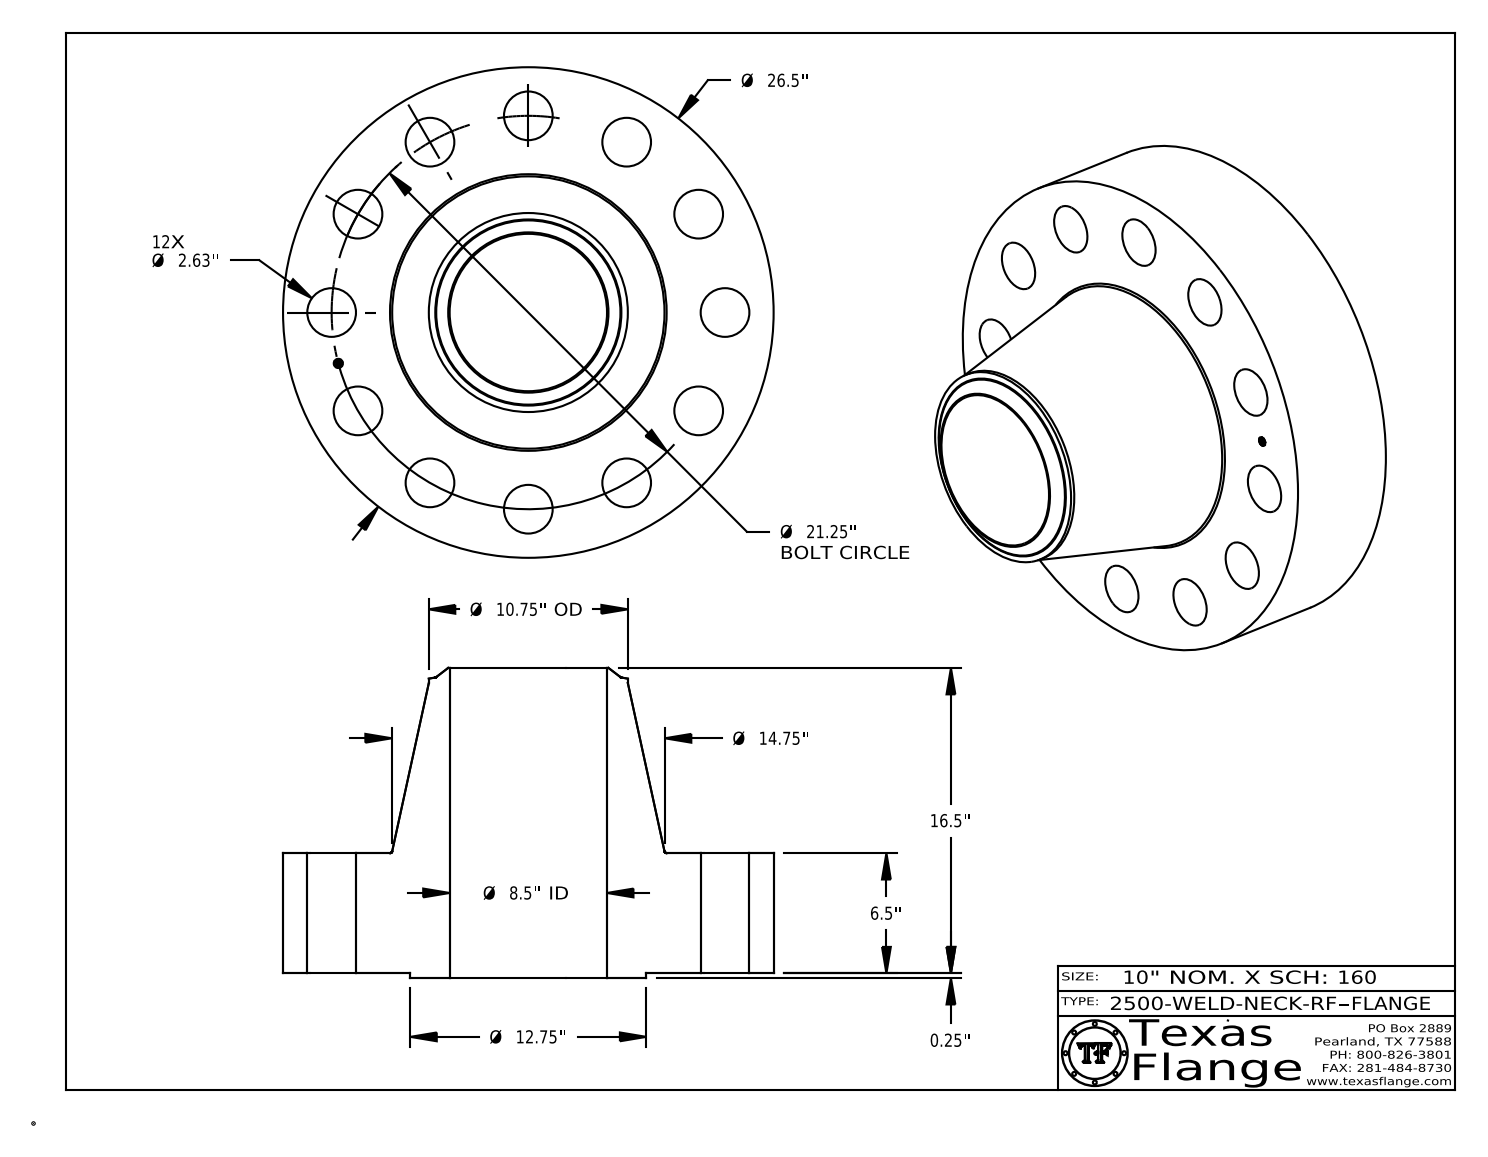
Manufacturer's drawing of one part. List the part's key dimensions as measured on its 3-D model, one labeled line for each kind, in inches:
Part name (STEP PRODUCT): 2500-WELD-NECK-RF
STEP written by: CATIA V5 STEP AP214 (AUTOMOTIVE_DESIGN)
Units: inches
Bodies: 1 solid, 431 faces (369 planar, 52 cylindrical, 10 other)
Overall size (bounding box): 26.5 × 26.5 × 16.75
Volume: 3 487 in³ · Surface area: 2 810 in²
Round holes (diameter × count): ⌀2.63 ×12, ⌀0.495 ×1, ⌀8.5 ×1
Round bosses / shafts (diameter × count): ⌀0.03 ×8, ⌀26.5 ×1, ⌀12.75 ×1, ⌀10.75 ×1, ⌀0.39 ×1
Main face-to-face distances: 6.5, 0.25, 6.75, 16.75, 16.5, 10, 6.735, 6.485, 0.015, 10.015
Hole centre spacings: 10.625, 5.5, 18.403, 15.026, 20.526, 15.026, 20.526, 21.25
